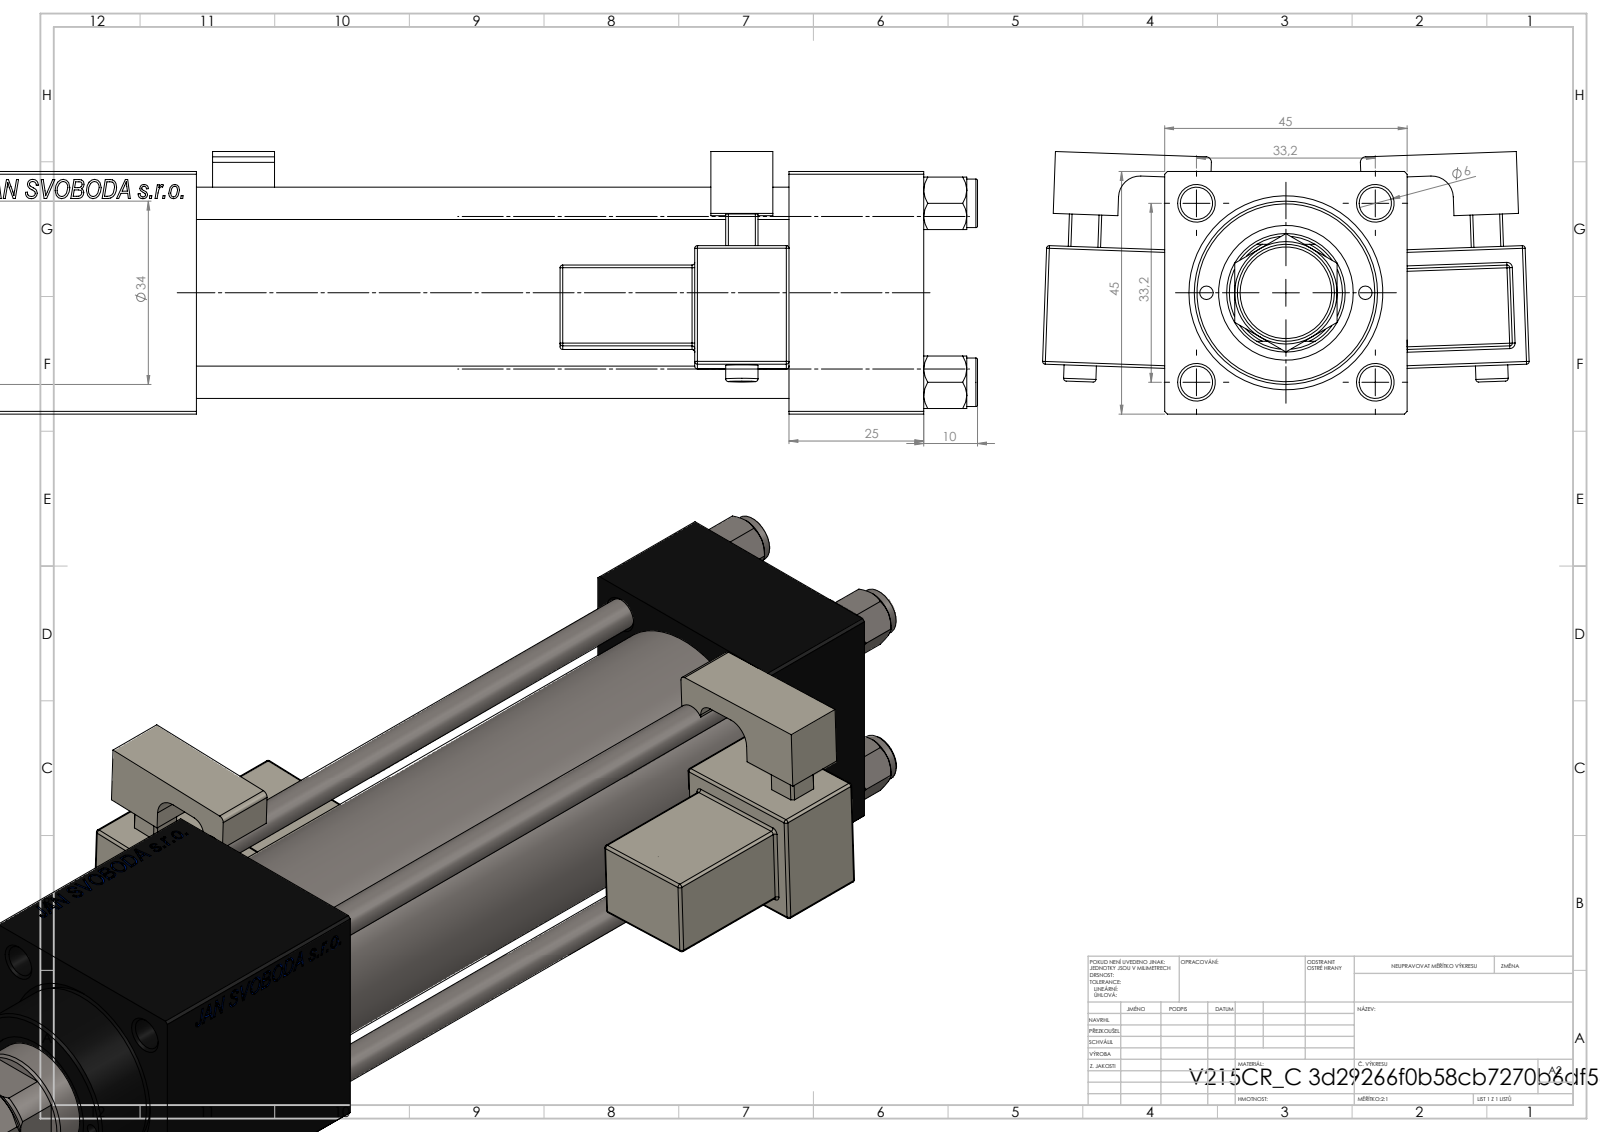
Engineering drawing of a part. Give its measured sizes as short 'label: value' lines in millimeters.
name: V215_VC_A; V215CR_MSU; V215CR_C_TYCINKA; V215CR_C_Body (+3 more)
written by: SolidWorks 2019 (CONFIG_CONTROL_DESIGN)
unit: mm
bodies: 14 solids, 1363 faces (605 planar, 154 cylindrical, 604 other)
size: 251 × 90.31 × 48.72
volume: 307 804 mm³; area: 108 133 mm²
holes: 4× ⌀6, 2× ⌀2.5, 2× ⌀7, 2× ⌀13.16, 2× ⌀20, 1× ⌀10.5, 1× ⌀22, 1× ⌀24, 1× ⌀25, 1× ⌀32, 1× ⌀33
bosses: 4× ⌀9, 2× ⌀6, 1× ⌀38, 1× ⌀34, 1× ⌀18, 1× ⌀11
rounds: 48× R0.5, 2× R1, 2× R2.5, 2× R4, 1× R10.5
face distances: 45, 25, 3, 135, 110, 183, 22.99, 92.5, 158, 13
hole spacings: 16.7, 23.48, 33.2, 35.47, 14.75, 46.95, 29.5, 135.5
